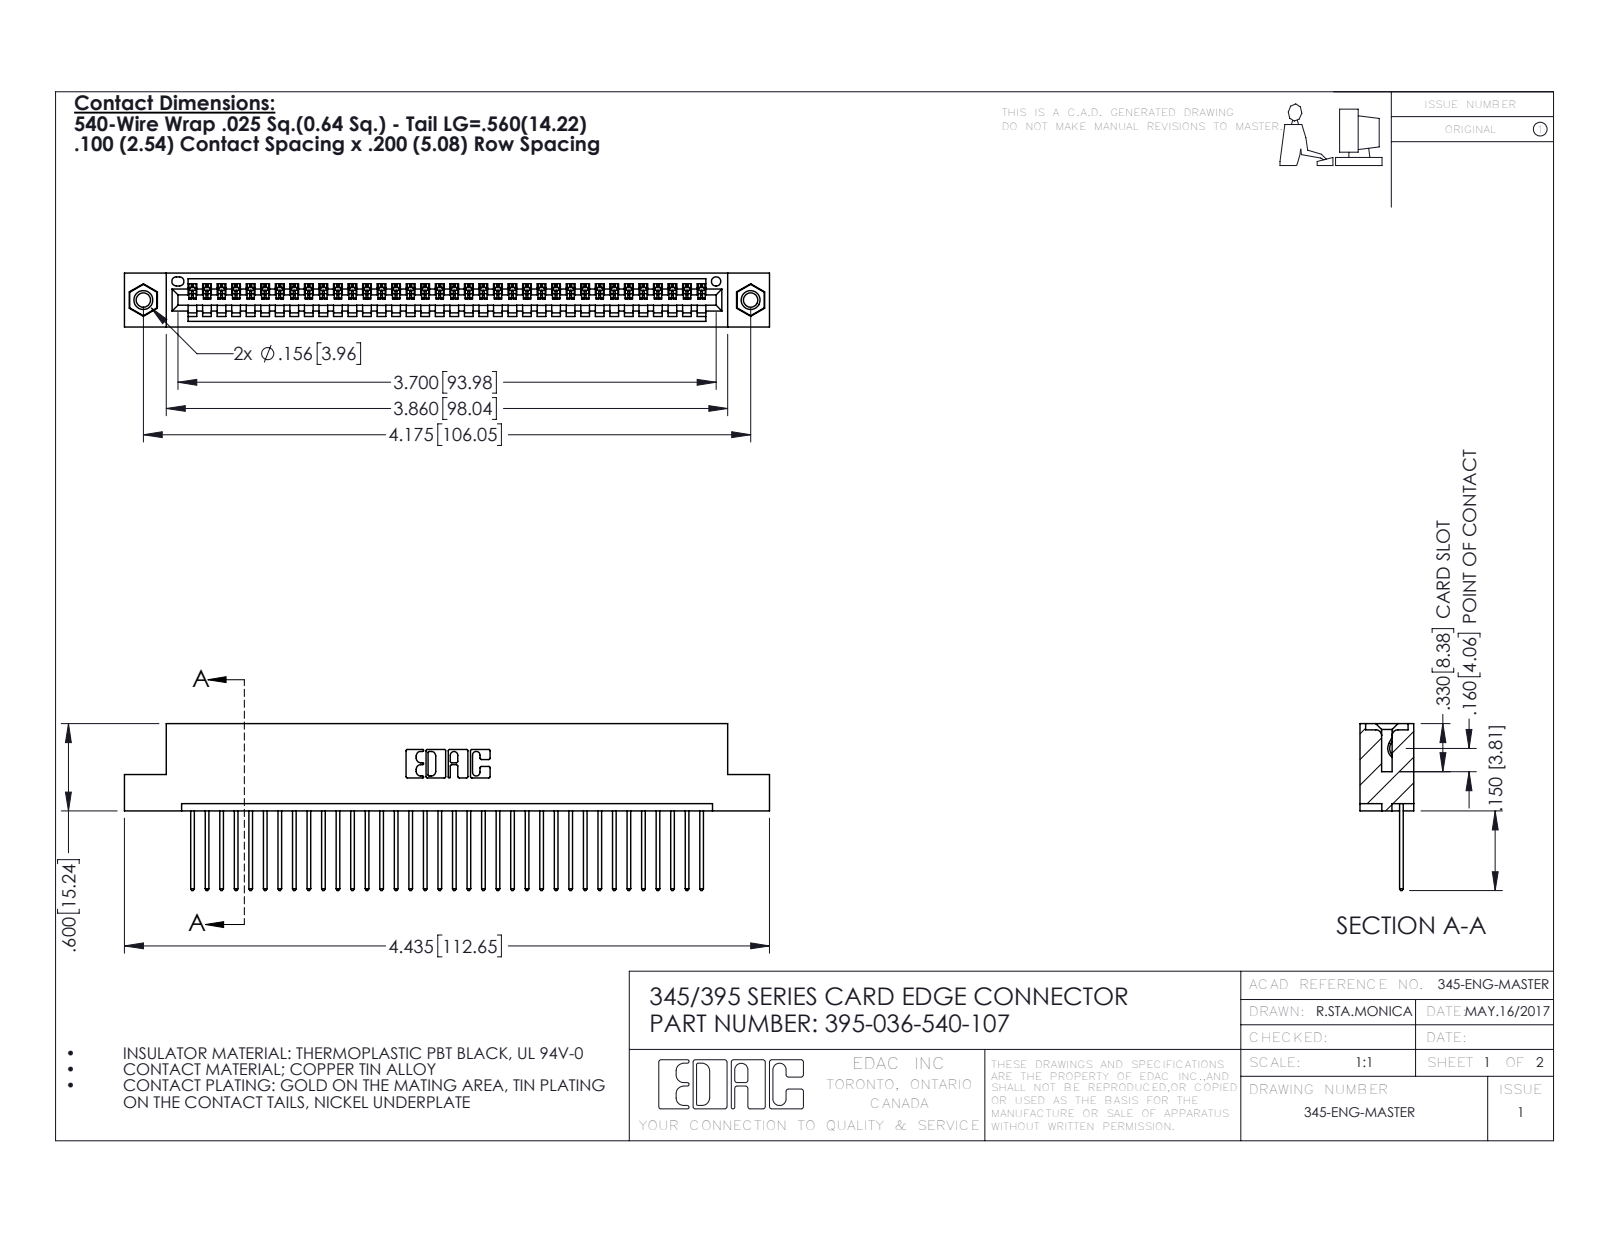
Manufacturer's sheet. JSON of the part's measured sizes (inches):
{"part_name": "345-292-001_345-293-140; 395-036-540-107; 345-250-001_345-250-005-103; 345 Part_Flush Mounting Lugs - 0.156 Dia-TI", "step_written_by": "SolidWorks 2016 (CONFIG_CONTROL_DESIGN)", "units": "inches", "bodies": {"solids": 39, "faces": 2274, "planar": 1552, "cylindrical": 706, "other": 16}, "overall_size": [4.435, 1.147, 0.37], "volume_in3": 0.652, "surface_area_in2": 22.48, "round_holes": [[0.098, 2], [0.125, 2], [0.156, 2], [0.064, 1]], "round_bosses_or_shafts": [[0.155, 2]], "partial_cylinders_radius": [[0.006, 72], [0.01, 72], [0.01, 22], [0.007, 6], [0.031, 6], [0.026, 3], [0.031, 2], [0.04, 2]], "face_to_face_distances": [0.072, 0.298, 0.37, 0.2, 0.098, 0.272, 0.025, 0.225, 0.149, 0.072], "hole_center_spacings": [0.27, 3.939, 4.175]}
